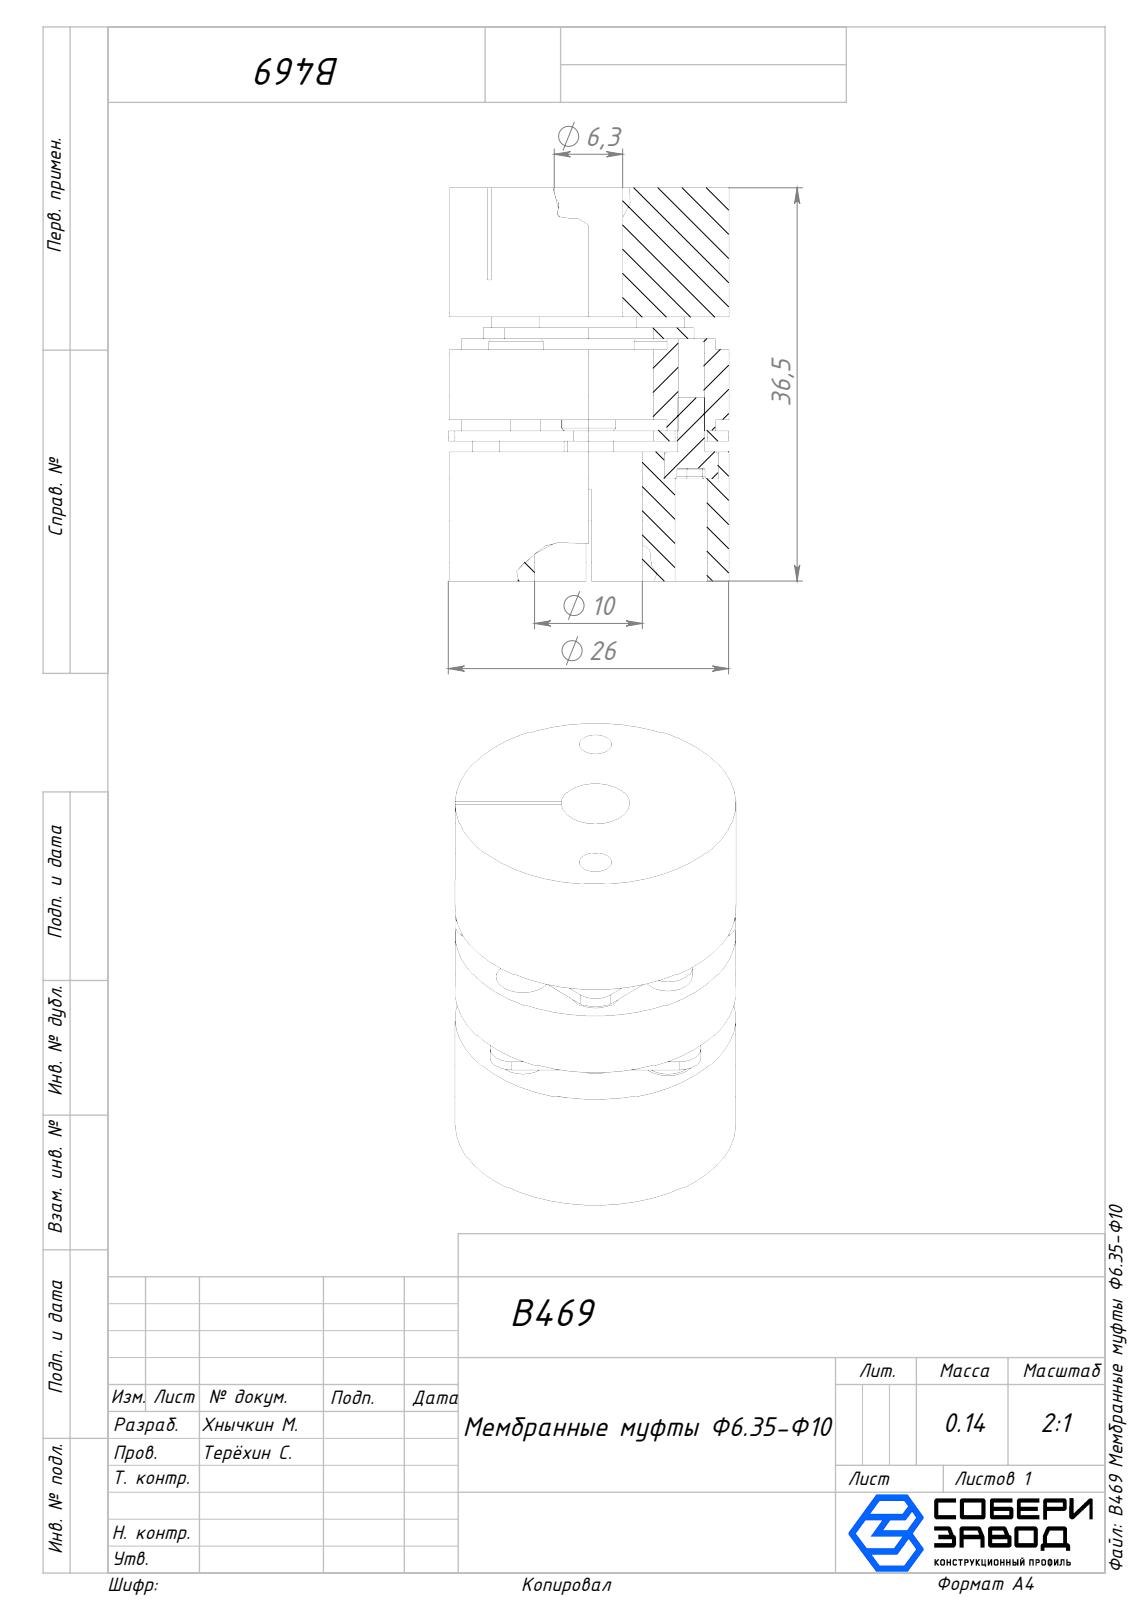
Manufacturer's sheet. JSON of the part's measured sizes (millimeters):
{"part_name": "Ниж.часть_00; Средняя часть_00; Винт_00; B469 Мембранные муфты Ф6.35-Ф10 (+1 more)", "step_written_by": "SolidWorks 2025 (AUTOMOTIVE_DESIGN)", "units": "millimeters", "bodies": {"solids": 11, "faces": 362, "planar": 120, "cylindrical": 226, "other": 16}, "overall_size": [36.5, 26, 26], "volume_mm3": 14035, "surface_area_mm2": 9763, "round_holes": [[3, 8], [5, 8], [2.4, 4], [6.35, 1], [10, 1], [12, 1]], "round_bosses_or_shafts": [[4.5, 8], [2.5, 8], [26, 1]], "partial_cylinders_radius": [[0.1, 48], [0.25, 48], [2, 8]], "face_to_face_distances": [1, 9.5, 2, 12, 10.5, 24.5, 14, 8.5, 15, 3], "hole_center_spacings": [7.27, 9.5, 13.44, 17.56, 19, 19.01]}
